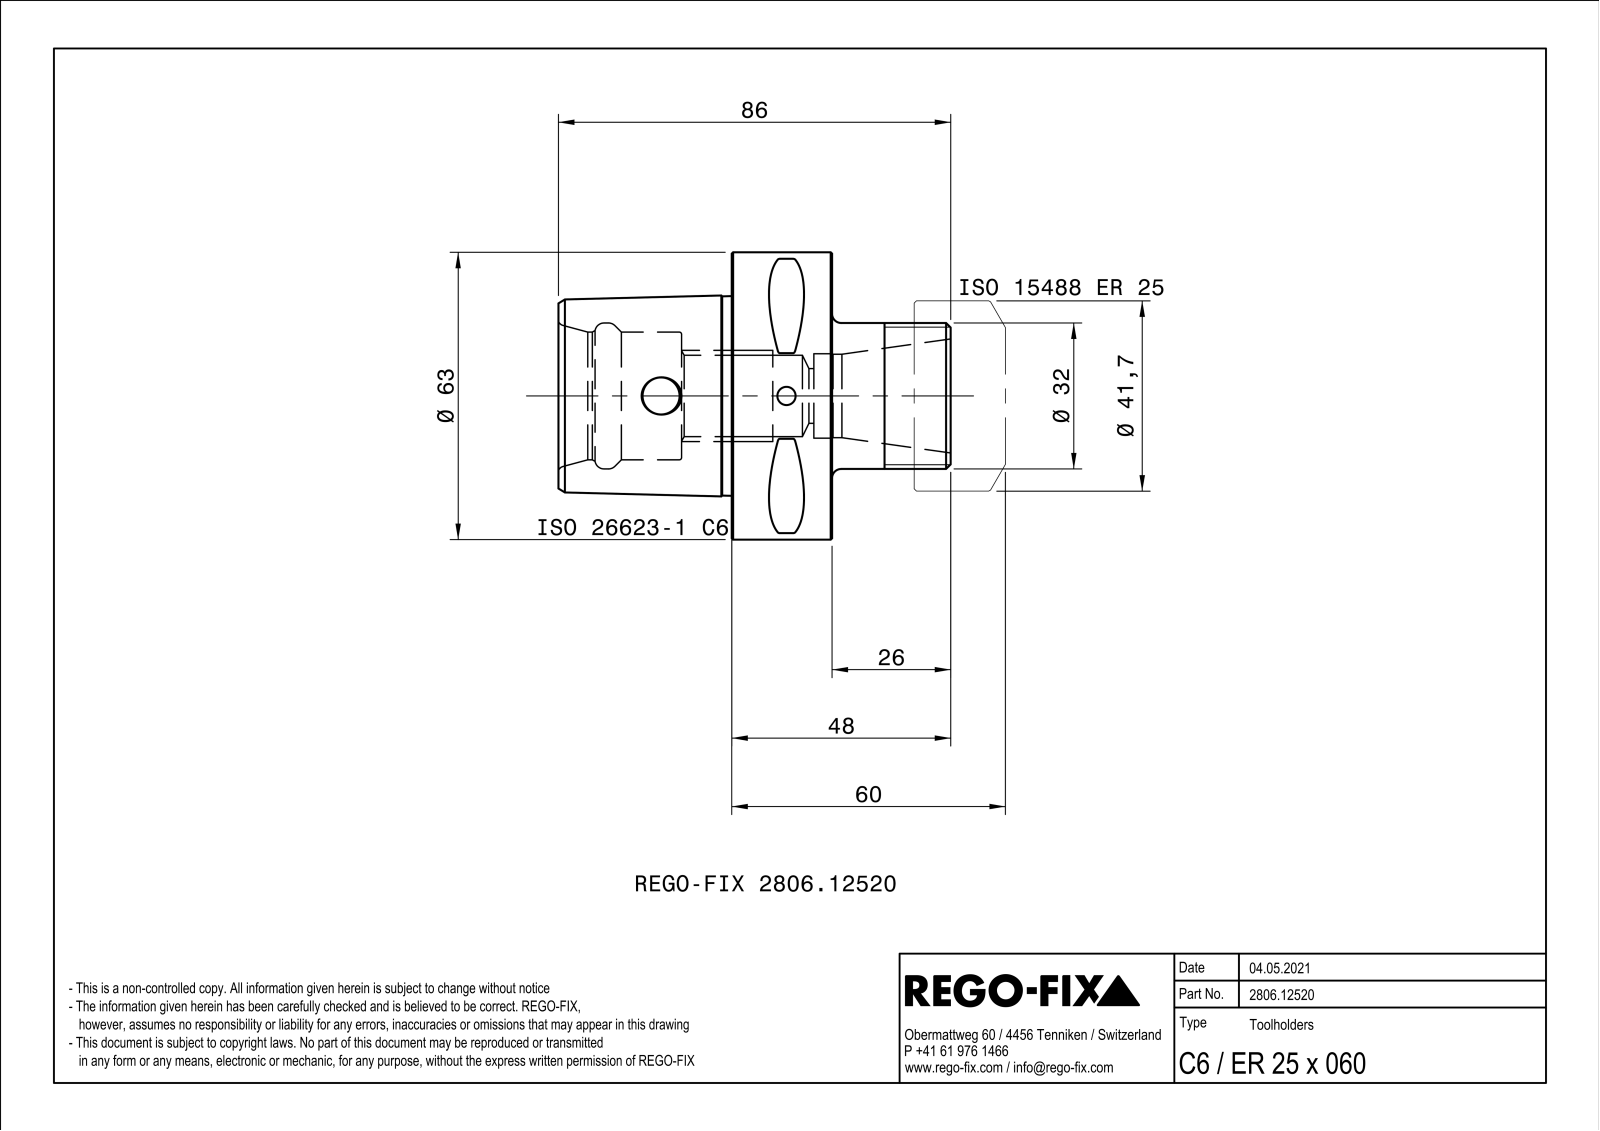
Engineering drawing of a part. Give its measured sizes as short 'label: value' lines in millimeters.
name: NOCUT
written by: SIEMENS PLM Software Solid Edge ST10 (AUTOMOTIVE_DESIGN)
unit: mm
bodies: 1 solid, 110 faces (21 planar, 23 cylindrical, 66 other)
size: 86 × 63 × 63
volume: 106 326 mm³; area: 24 001 mm²
holes: 1× ⌀4, 1× ⌀8.1, 1× ⌀12, 1× ⌀17.84, 1× ⌀18.3, 1× ⌀18.5, 1× ⌀28
bosses: 1× ⌀63, 1× ⌀32
rounds: 8× R0.5, 1× R5
face distances: 22, 60, 38, 24.89, 33, 11, 27, 26, 48, 59
hole spacings: 27.5
